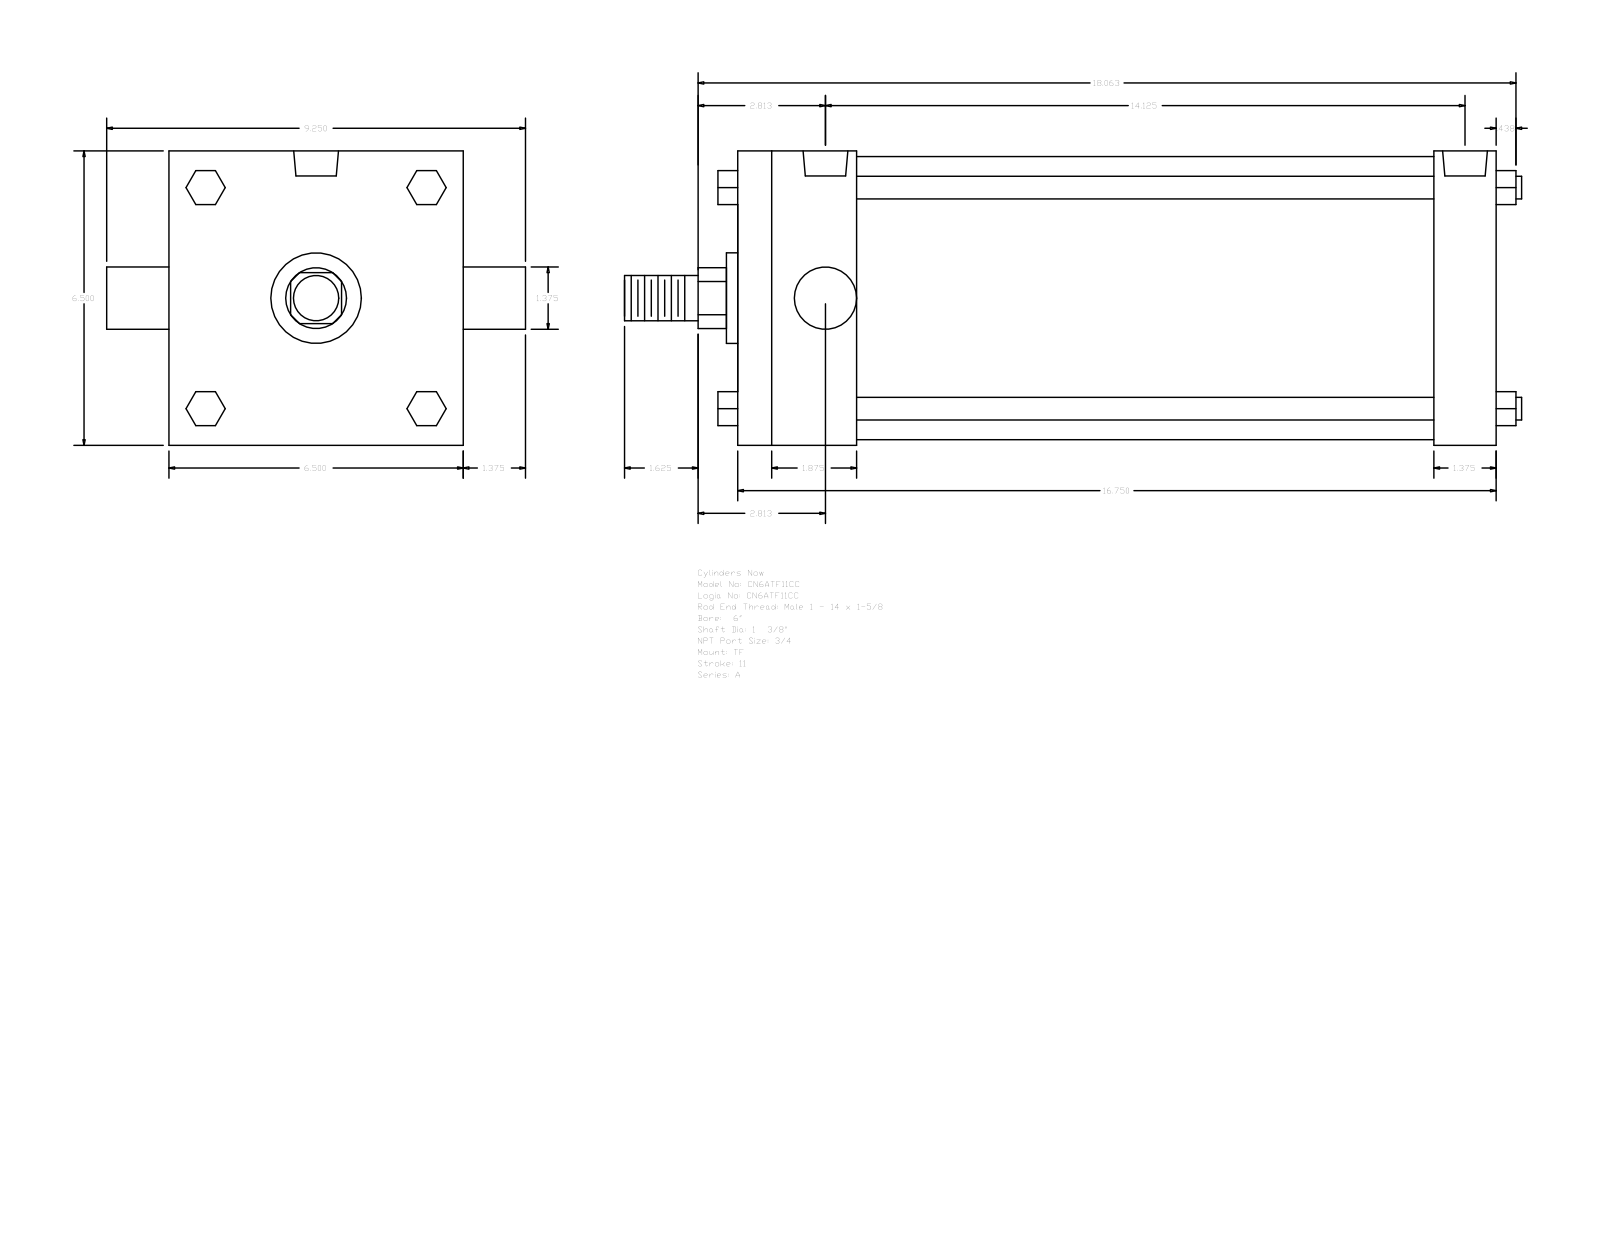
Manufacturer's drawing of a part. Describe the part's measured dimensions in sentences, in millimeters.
The part is named "A_TF__0600_1.375". Its 3-D file was written by "GSSL Pune (CONFIG_CONTROL_DESIGN)". It is 0 solids with 120 faces: 92 planar, 28 cylindrical and 0 other. Overall it measures 503.24 by 234.95 by 165.1 millimeters. Round holes: 3 of diameter 15.08, 2 of diameter 25.12. Round bosses or shafts: 4 of diameter 12.7, 2 of diameter 34.92, 1 of diameter 158.75, 1 of diameter 50.8, 1 of diameter 25.4. Partial cylindrical surfaces (rounded edges, fillets, slot ends): 1 of radius 17.06. The main face-to-face distances are 165.1, 425.45, 66.67, 358.78, 390.52, 323.85, 34.93, 19.05, 61.97, 107.34. The hole center spacings are 5.56, 353.21, 347.65, 358.77.
